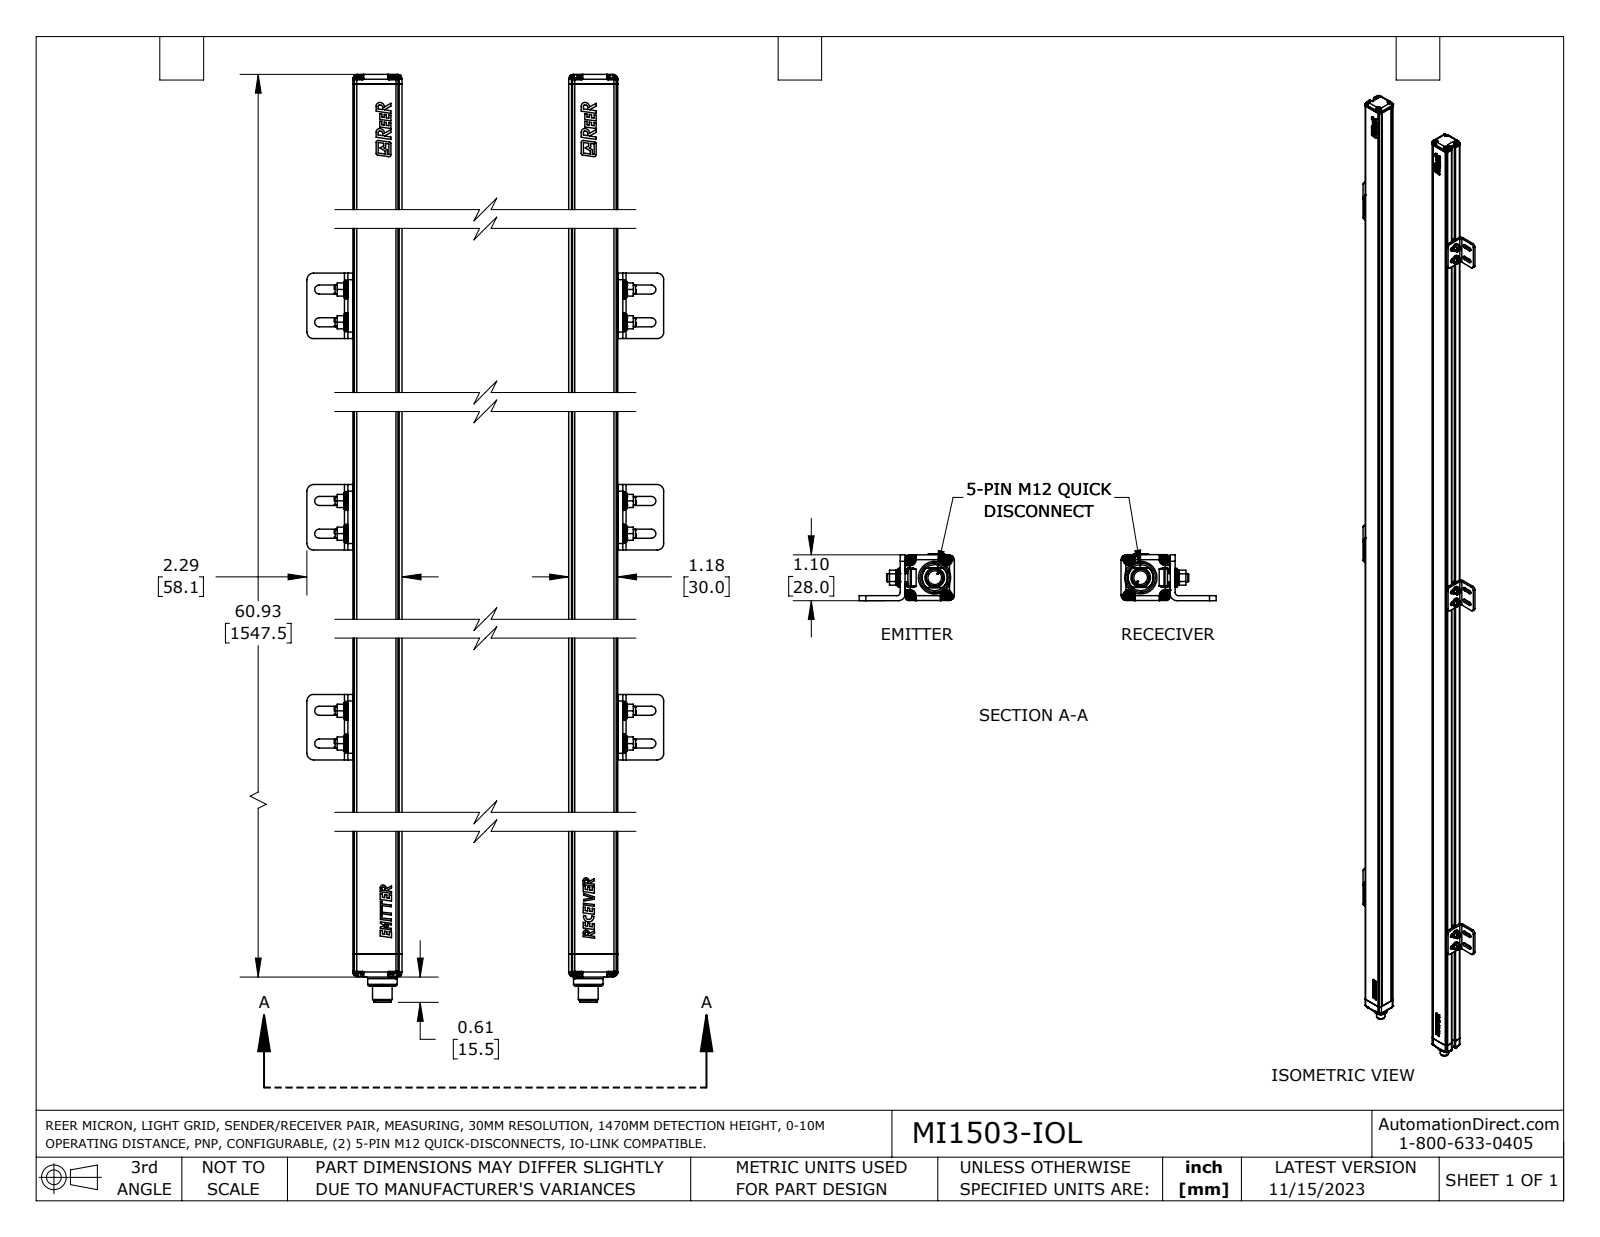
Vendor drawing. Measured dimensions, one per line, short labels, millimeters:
name: MI1501-IOL_MI1503-IOL_EMITTER; MI1501-IOL_MI1503-IOL; MI1501-IOL_MI1503-IOL_RECEIVER
written by: SolidWorks 2023 (AUTOMOTIVE_DESIGN)
unit: mm
bodies: 76 solids, 2668 faces (1218 planar, 1066 cylindrical, 384 other)
size: 1563.4 × 167 × 28
volume: 921 900 mm³; area: 963 900 mm²
holes: 20× ⌀5, 12× ⌀6, 12× ⌀7.1, 8× ⌀2.6, 8× ⌀3, 2× ⌀8.4, 2× ⌀9.9, 2× ⌀10.3
bosses: 16× ⌀1.2, 16× ⌀0.7, 12× ⌀11.4, 12× ⌀9.7, 8× ⌀3.5, 8× ⌀2.5, 2× ⌀18, 2× ⌀12
rounds: 122× R0.5, 120× R0.3, 64× R0.4, 48× R2.7, 32× R0.4, 26× R4, 24× R0.1, 24× R3
face distances: 1.5, 21.5, 23, 3.3, 28, 54.1, 3.5, 26.5, 75.6, 105.6
hole spacings: 20, 22, 586.2, 587.7, 1173.9, 13, 18.6, 31.1
